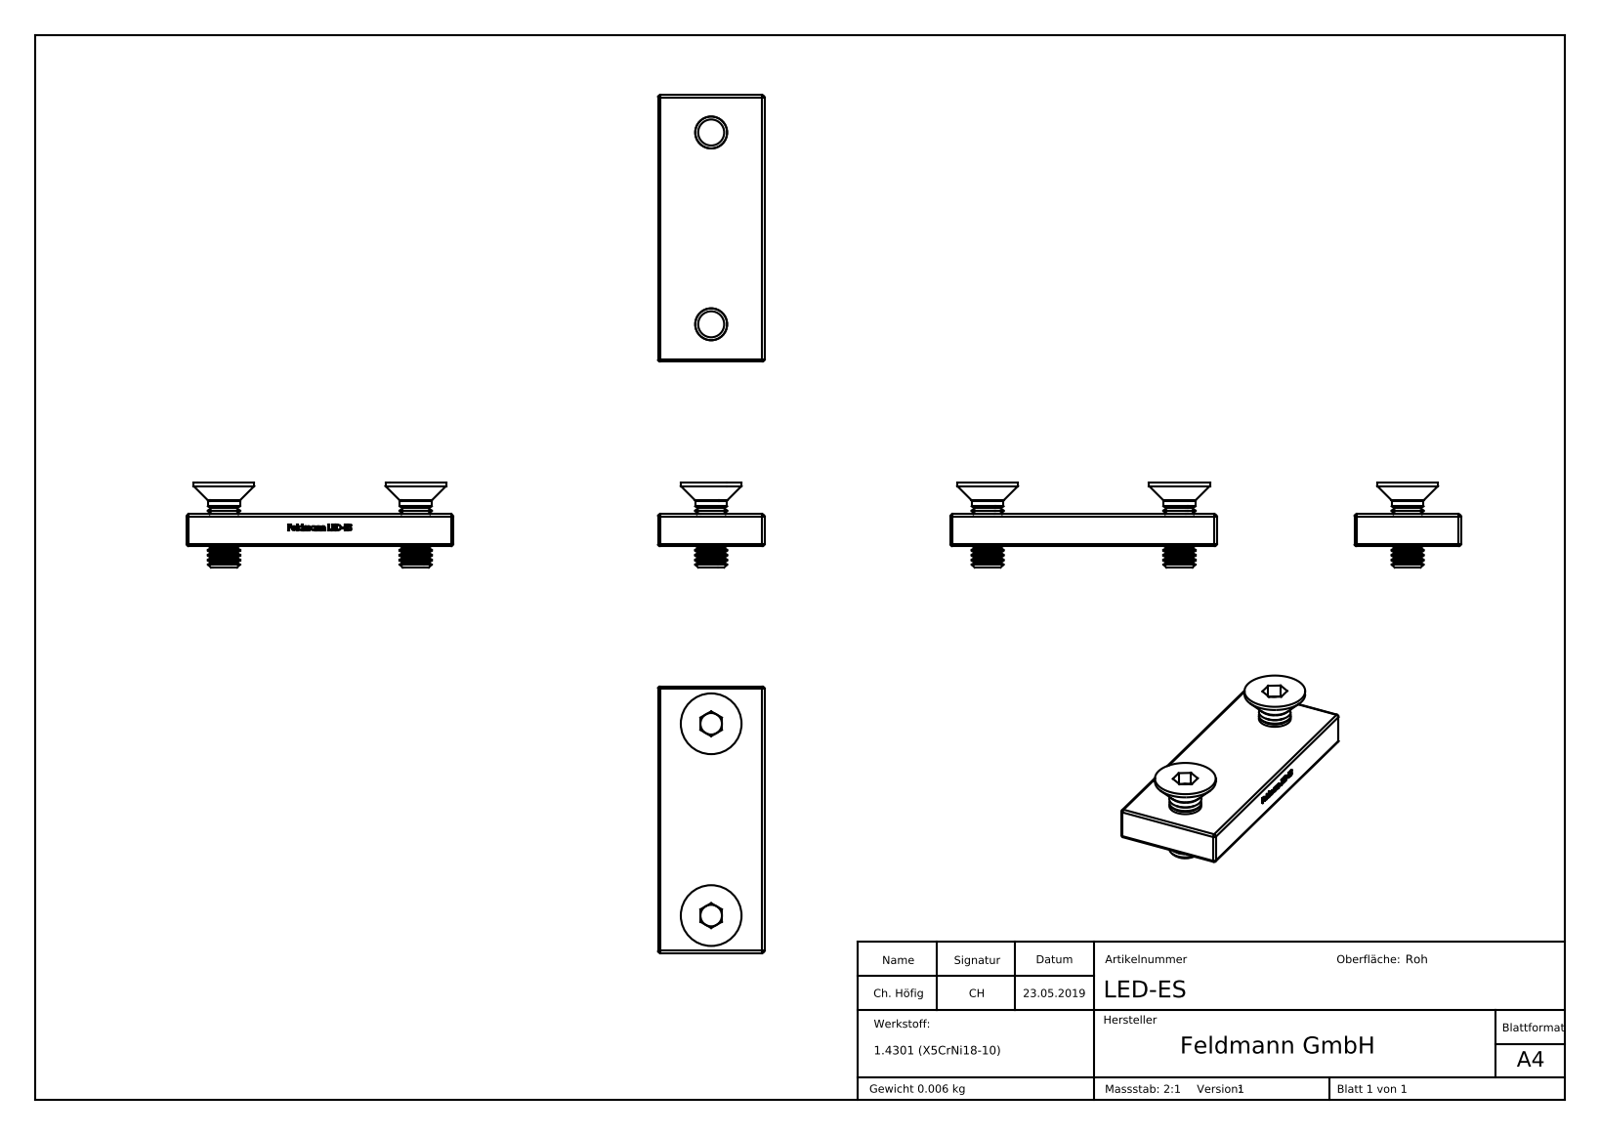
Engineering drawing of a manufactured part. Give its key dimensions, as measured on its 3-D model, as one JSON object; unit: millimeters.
{"part_name": "socket countersunk head screw_din_DIN 7991 - M3 x 8 --- 8S; LED-ES; LED-ES Teil1_LED-ES Teil1", "step_written_by": "SolidWorks 2015 (CONFIG_CONTROL_DESIGN)", "units": "millimeters", "bodies": {"solids": 3, "faces": 414, "planar": 148, "cylindrical": 68, "other": 198}, "overall_size": [25, 10, 8], "volume_mm3": 844, "surface_area_mm2": 1038, "round_holes": [[2.5, 2]], "round_bosses_or_shafts": [[5.7, 2], [3, 2]], "partial_cylinders_radius": [[0.2, 12]], "face_to_face_distances": [3, 10, 6, 25, 2, 5, 8, 2.02, 15.58, 3.99], "hole_center_spacings": [18]}
